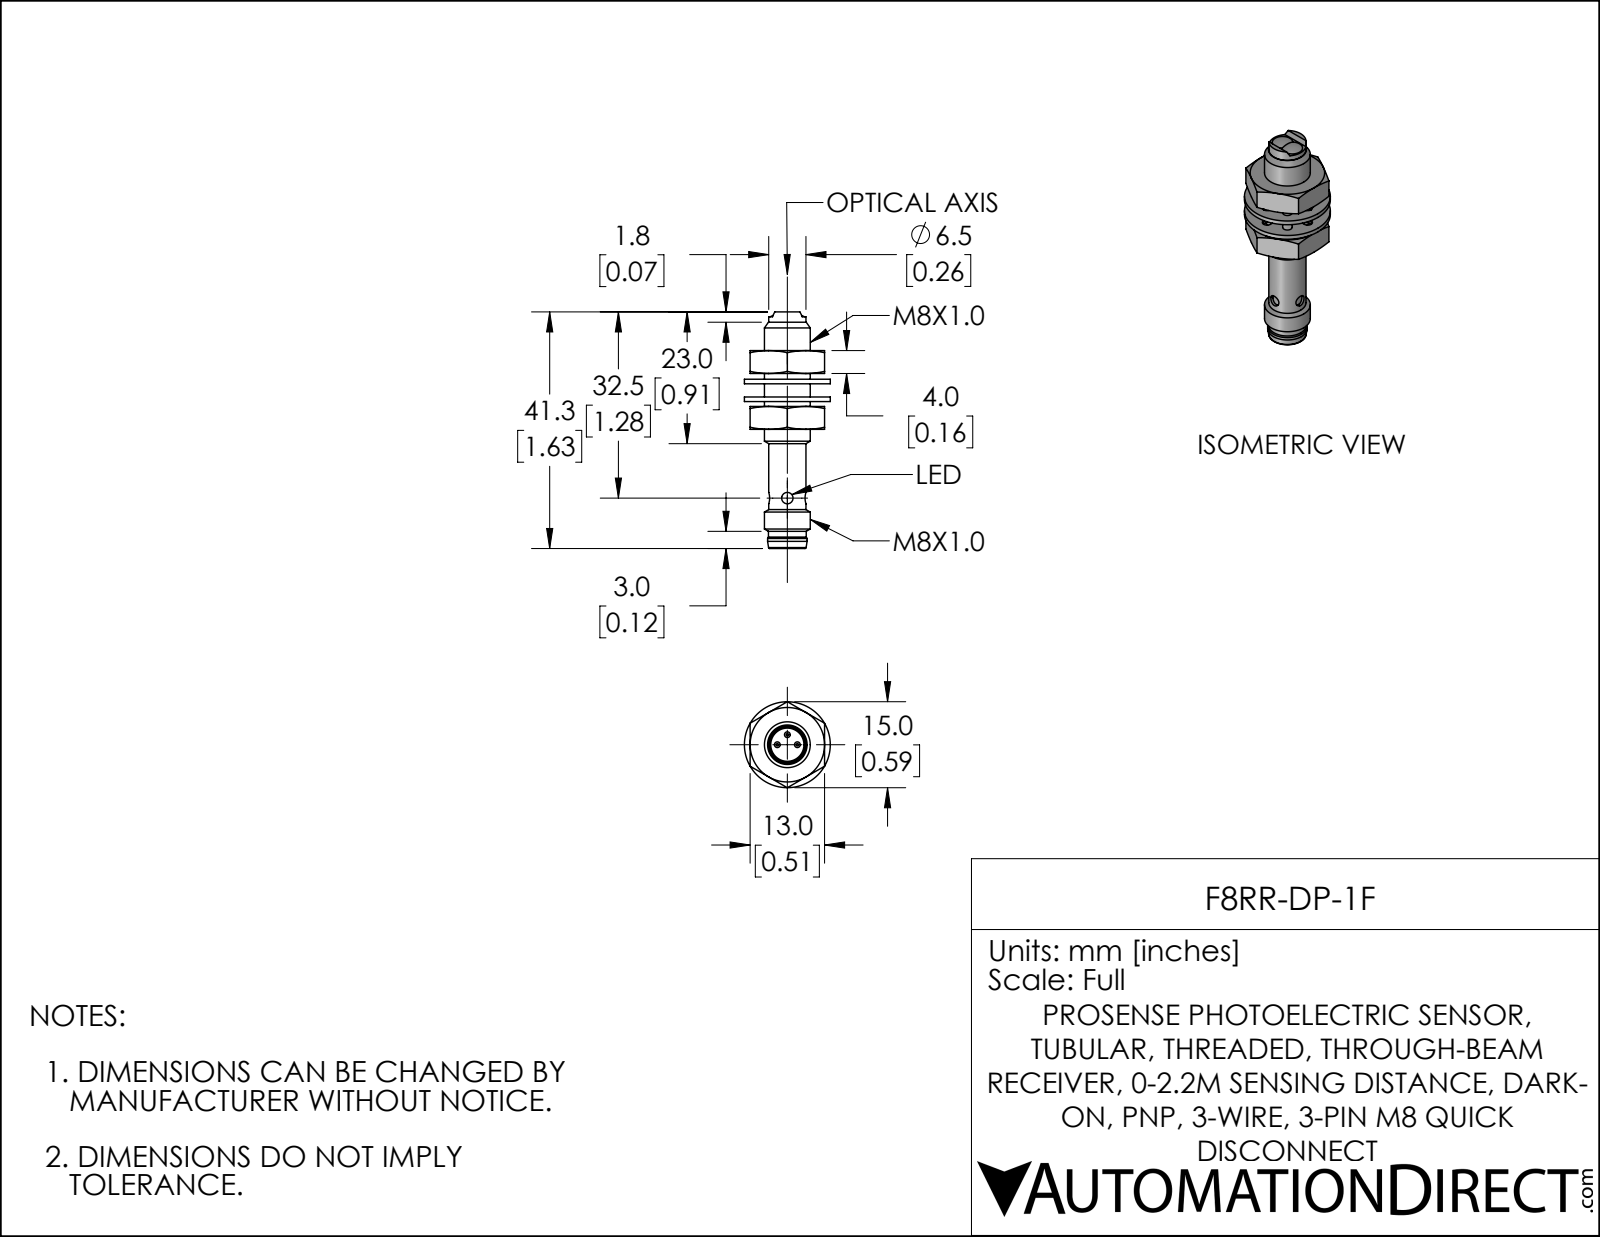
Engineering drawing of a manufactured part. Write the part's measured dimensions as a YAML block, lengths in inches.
part_name: "F8RR-DP-1F"
step_written_by: "SolidWorks 2019 (CONFIG_CONTROL_DESIGN)"
units: inches
bodies: {solids: 5, faces: 157, planar: 63, cylindrical: 54, other: 40}
overall_size: [1.626, 0.591, 0.591]
volume: 0.162
surface_area: 4.169
round_holes:
  - {diameter: 0.079, count: 2}
  - {diameter: 0.228, count: 1}
  - {diameter: 0.272, count: 1}
round_bosses_or_shafts:
  - {diameter: 0.039, count: 3}
  - {diameter: 0.591, count: 1}
  - {diameter: 0.315, count: 1}
  - {diameter: 0.272, count: 1}
  - {diameter: 0.26, count: 1}
  - {diameter: 0.256, count: 1}
partial_cylinders:
  - {radius: 0.032, count: 8}
  - {radius: 0.109, count: 1}
  - {radius: 0.165, count: 1}
face_to_face_distances: [0.122, 0.031, 0.512, 0.384, 0.157, 0.154, 0.091, 0.033, 0.065, 0.197]
